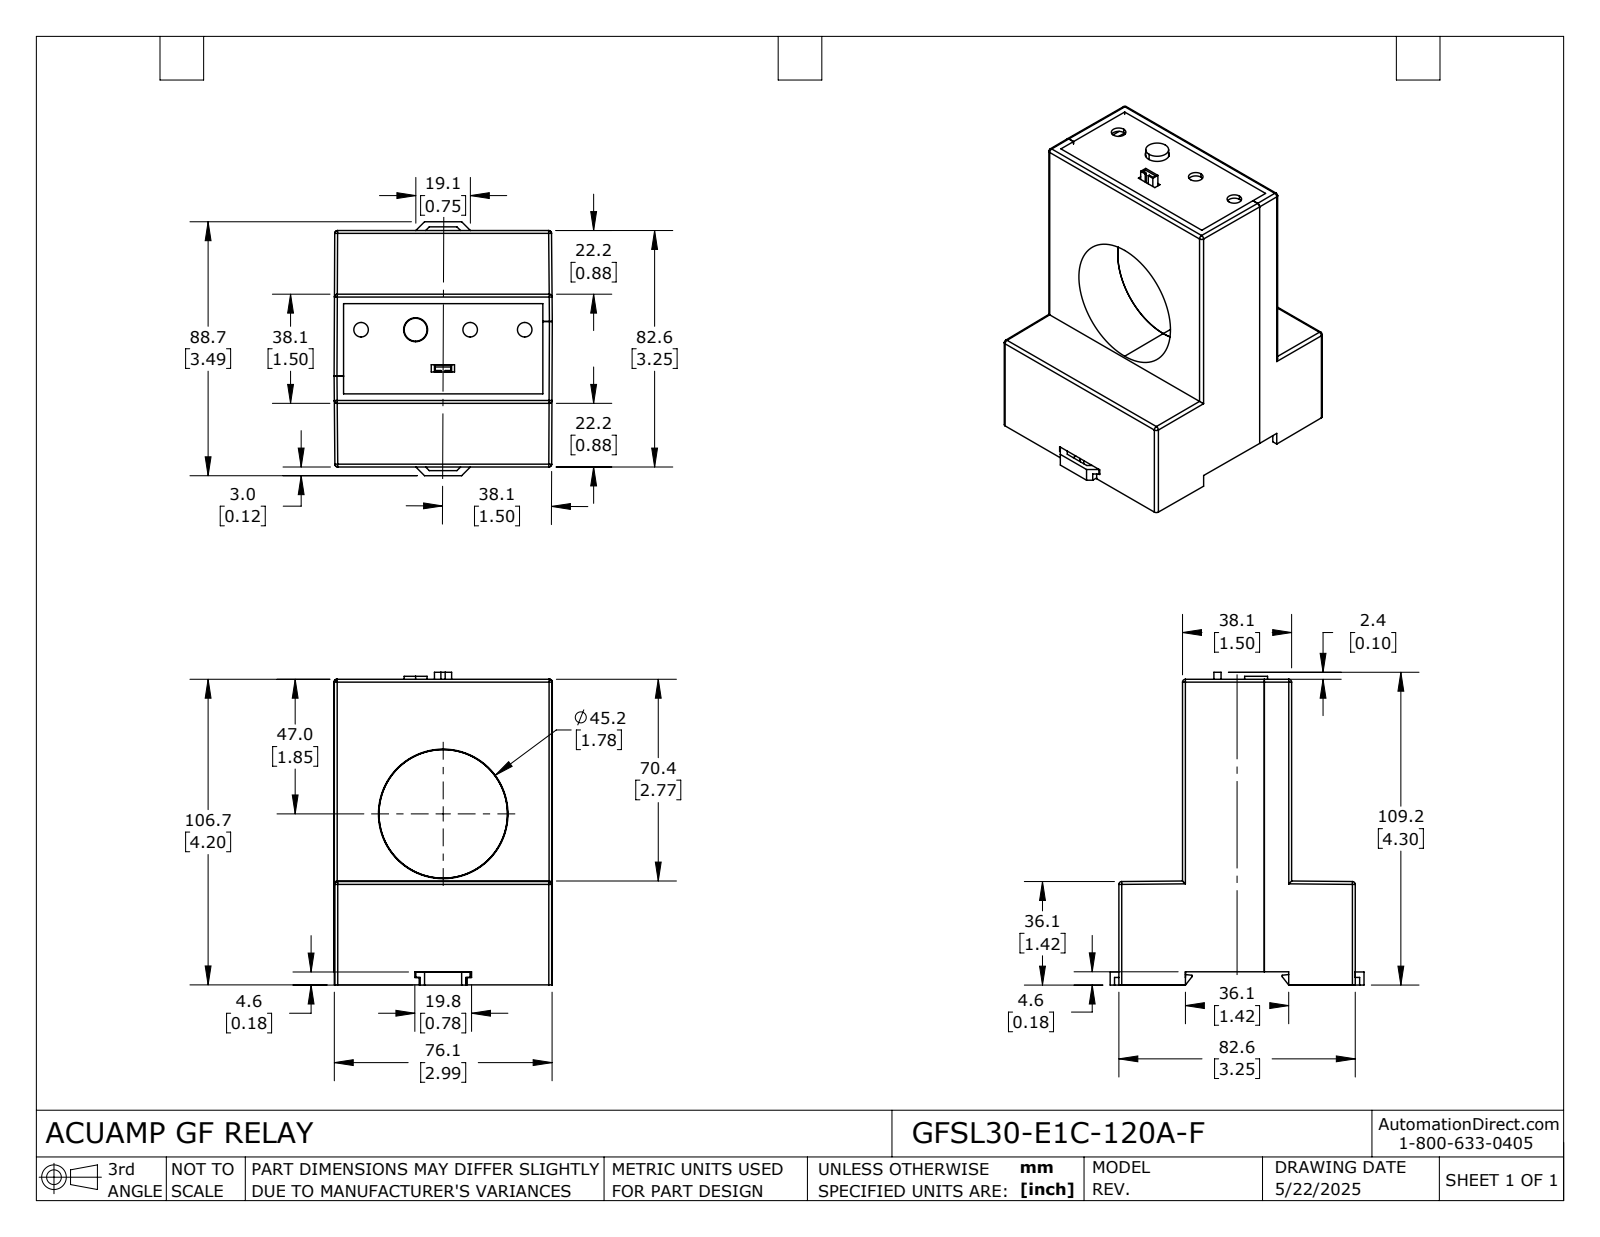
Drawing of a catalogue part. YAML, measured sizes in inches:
part_name: "GFSL30-E1C-120A-F"
step_written_by: "SolidWorks 2024 (AUTOMOTIVE_DESIGN)"
units: inches
bodies: {solids: 8, faces: 1046, planar: 890, cylindrical: 120, other: 36}
overall_size: [4.299, 3.49, 3]
volume: 5.534
surface_area: 153.9
round_holes:
  - {diameter: 0.2, count: 7}
  - {diameter: 0.33, count: 4}
  - {diameter: 0.12, count: 2}
round_bosses_or_shafts:
  - {diameter: 0.1, count: 2}
  - {diameter: 0.315, count: 1}
partial_cylinders:
  - {radius: 0.02, count: 23}
  - {radius: 0.039, count: 20}
  - {radius: 0.008, count: 4}
  - {radius: 0.012, count: 4}
  - {radius: 0.104, count: 4}
  - {radius: 0.18, count: 4}
face_to_face_distances: [0.08, 0.875, 2.295, 1.42, 2.916, 0.08, 2.996, 1.5, 0.795, 2.215]
hole_center_spacings: [0.75, 0.919, 1.5, 0.531, 1.591, 2.25, 2.312, 0.993]
